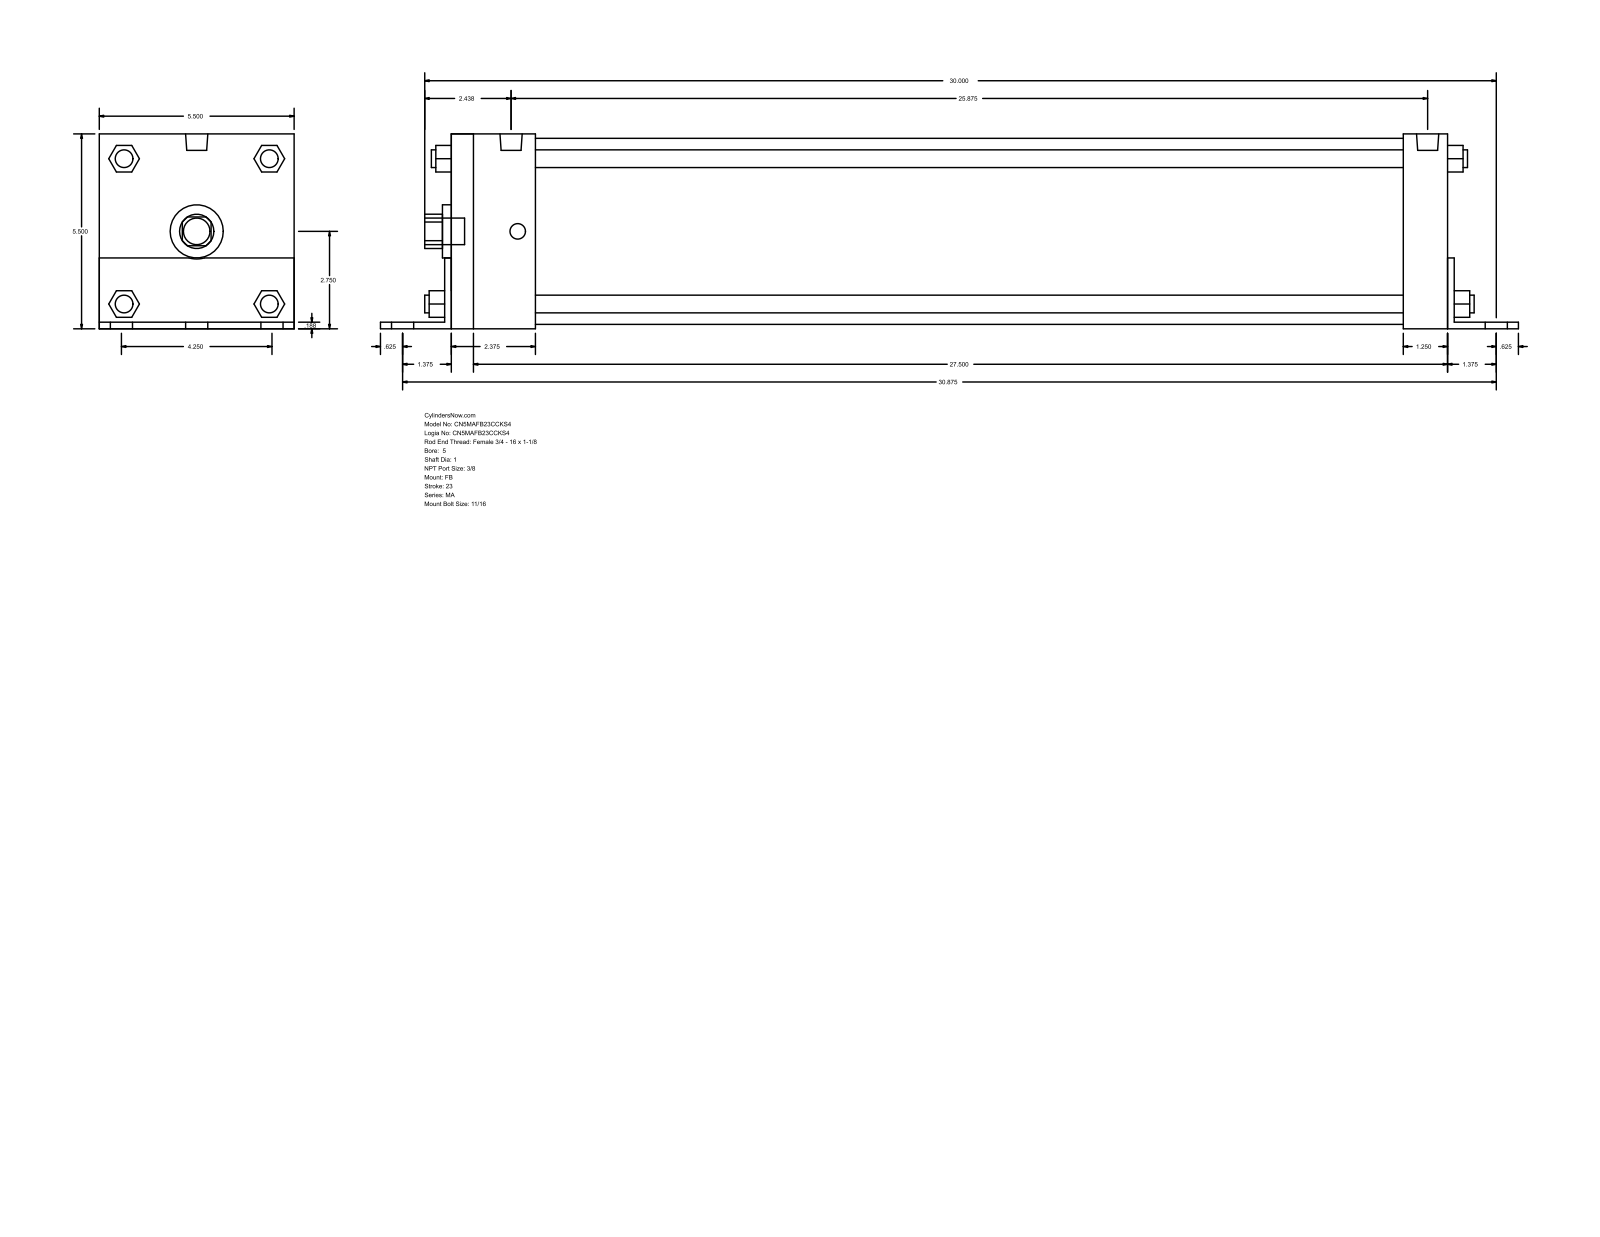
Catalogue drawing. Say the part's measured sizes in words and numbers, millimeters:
The part is named "MA_FB__0500_1". Its 3-D file was written by "GSSL Pune (CONFIG_CONTROL_DESIGN)". It is 0 solids with 140 faces: 105 planar, 35 cylindrical and 0 other. Overall it measures 815.98 by 139.75 by 139.7 millimeters. Round holes: 1 of diameter 25.4, 1 of diameter 38.1, 1 of diameter 133.35. Round bosses or shafts: 6 of diameter 17.46, 4 of diameter 12.7, 4 of diameter 11.11, 2 of diameter 15.93, 1 of diameter 19.05. Partial cylindrical surfaces (rounded edges, fillets, slot ends): 1 of radius 12.29, 1 of radius 19.81. The main face-to-face distances are 139.7, 4.76, 139.75, 4.71, 134.99, 714.37, 4.77, 719.14, 719.13, 723.9.
